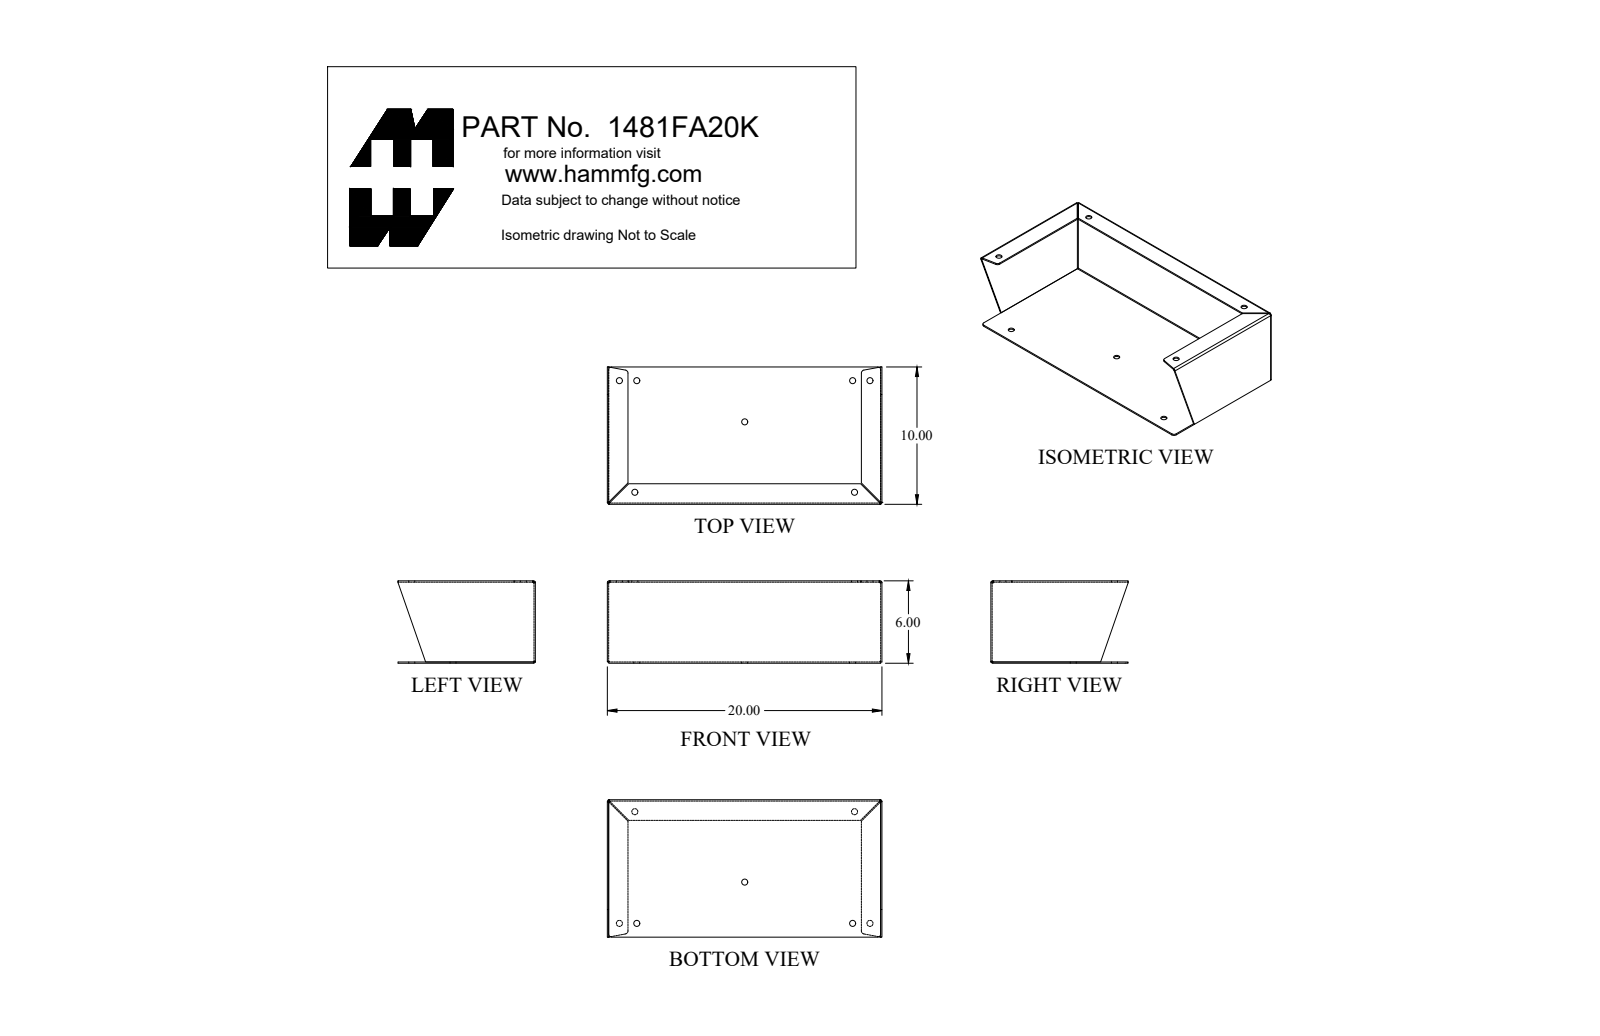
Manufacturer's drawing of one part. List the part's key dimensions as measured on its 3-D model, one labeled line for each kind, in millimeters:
Part name (STEP PRODUCT): 1481FA20K_Default
STEP written by: SolidWorks 2019 (CONFIG_CONTROL_DESIGN)
Units: millimetres
Bodies: 1 solid, 78 faces (42 planar, 30 cylindrical, 6 other)
Overall size (bounding box): 508 × 254 × 152.4
Volume: 729 400 mm³ · Surface area: 612 100 mm²
Round holes (diameter × count): ⌀11.1 ×7
Partial cylindrical surfaces — rounded edges, fillets, slot ends (radius × count): R1.2 ×6, R3.6 ×6, R5.6 ×4
Main face-to-face distances: 2.4, 2.4, 505.6, 508, 503.2, 147.6, 150, 150, 152.4, 38.1
Hole centre spacings: 32.2, 206.4, 208.3, 213.7, 241.3, 244, 431.4, 452.6
